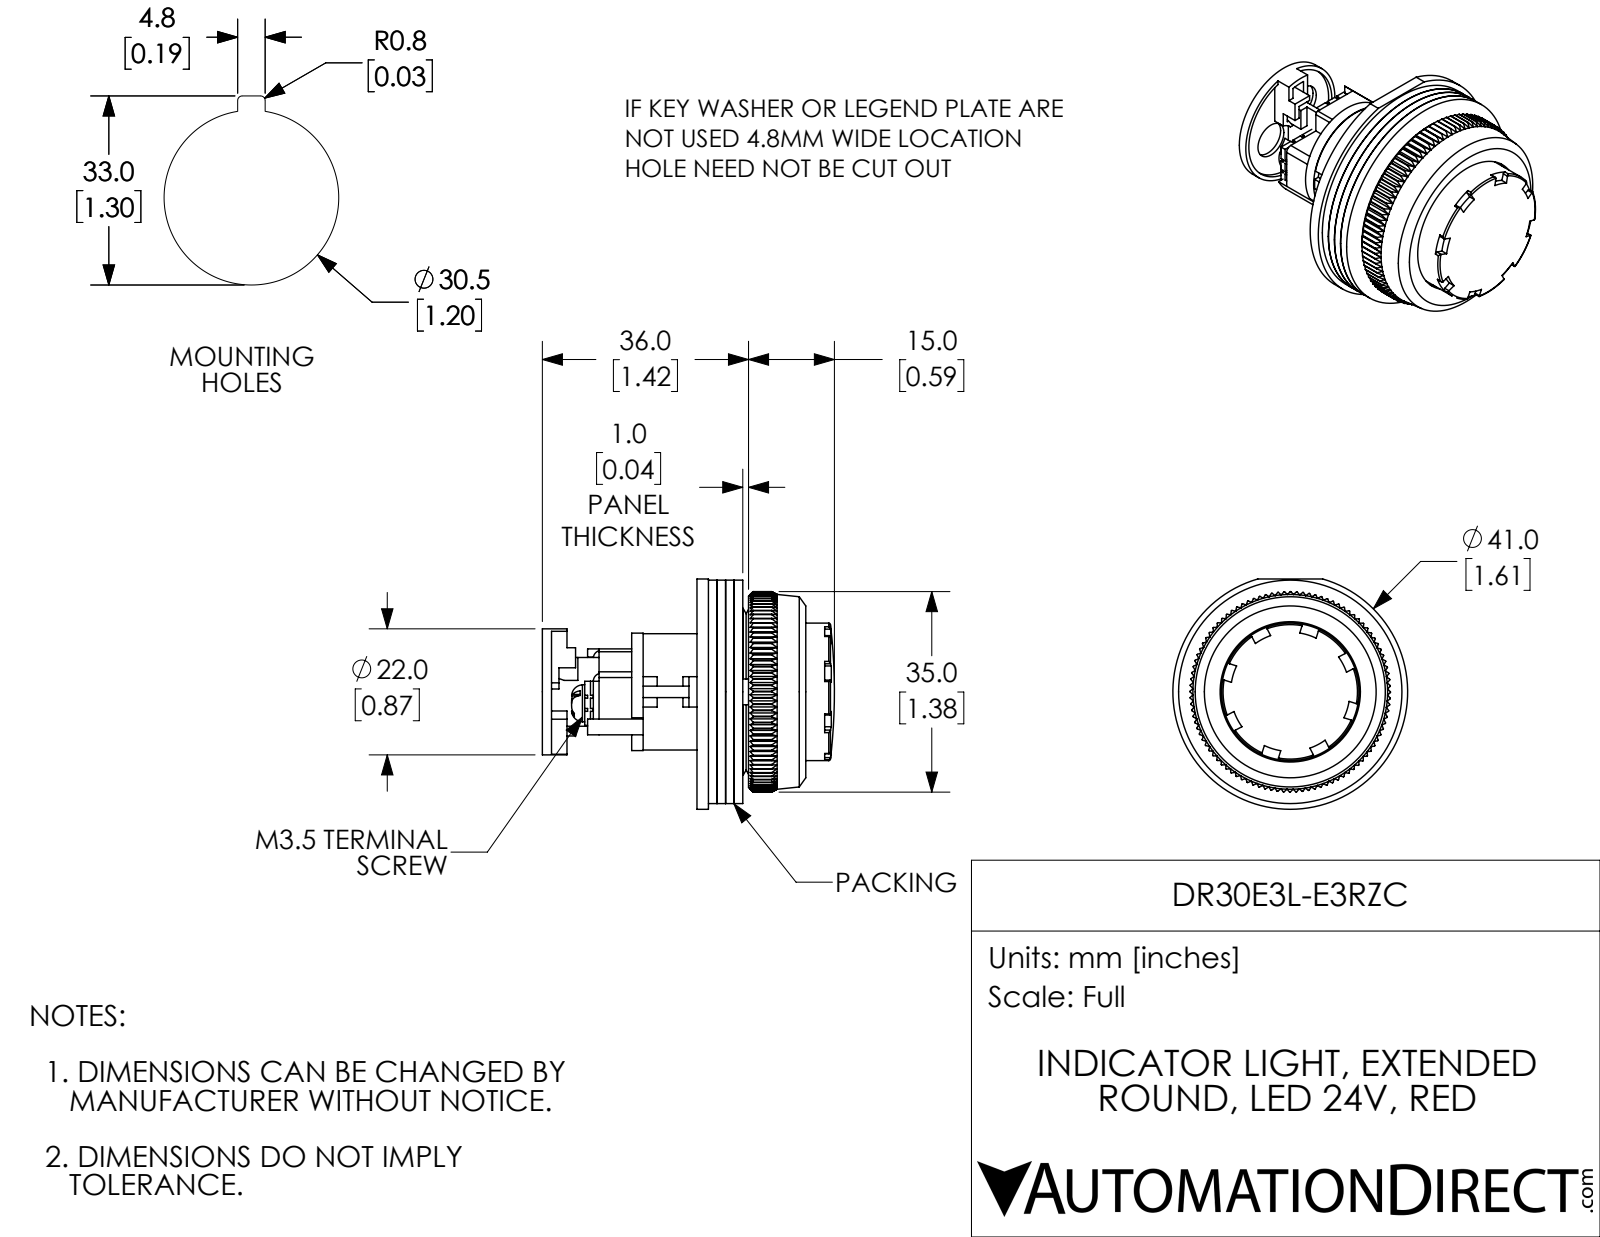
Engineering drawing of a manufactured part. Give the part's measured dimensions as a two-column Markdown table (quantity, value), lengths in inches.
| quantity | value |
| --- | --- |
| part name | DR30E3L-E3RZC |
| STEP written by | SolidWorks 2017 (AUTOMOTIVE_DESIGN) |
| units | inches |
| bodies | 16 solids, 1287 faces (717 planar, 328 cylindrical, 242 other) |
| overall size | 2.008 × 1.614 × 1.583 |
| volume | 1.072 in³ |
| surface area | 37.55 in² |
| round holes (diameter × count) | 0.118 × 2, 0.138 × 2, 0.252 × 2, 0.563 × 1, 0.63 × 1, 0.72 × 1, 0.787 × 1, 0.807 × 1, 0.866 × 1, 0.965 × 1, 1.122 × 1, 1.173 × 1 |
| round bosses / shafts (diameter × count) | 0.063 × 2, 1.614 × 1, 1.535 × 1, 1.16 × 1, 0.945 × 1, 0.858 × 1, 0.819 × 1, 0.799 × 1 |
| partial cylindrical surfaces (radius × count) | 0.012 × 16, 0.059 × 8, 0.01 × 5, 0.022 × 5, 0.016 × 4, 0.055 × 4, 0.02 × 2, 0.039 × 2 |
| main face-to-face distances | 0.059, 0.118, 0.177, 0.039, 0.197, 0.079, 0.315, 0.256, 0.098, 0.236 |
| hole center spacings | 0.176, 0.185, 0.361, 0.352, 0.37 |
